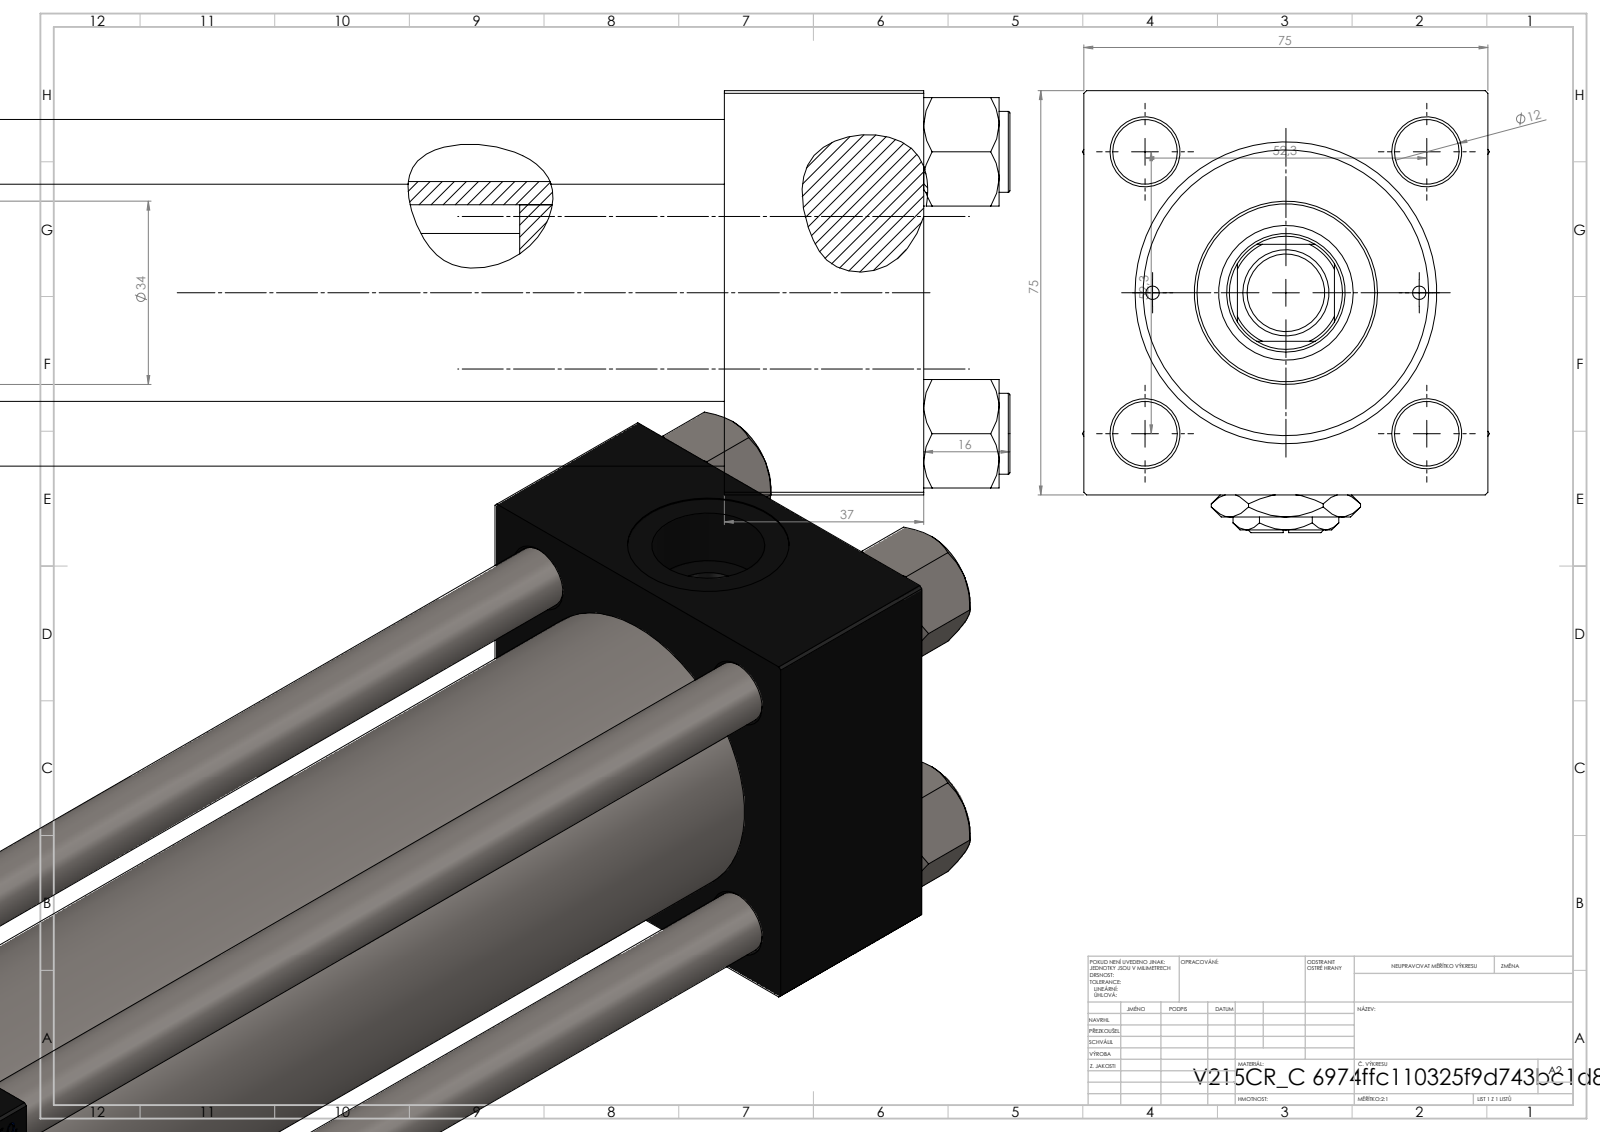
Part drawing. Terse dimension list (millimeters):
name: ROD_END_AH; V215_VC_A; NUT_M5_C; V215CR_C_Body (+3 more)
written by: SolidWorks 2019 (CONFIG_CONTROL_DESIGN)
unit: mm
bodies: 13 solids, 1216 faces (555 planar, 99 cylindrical, 562 other)
size: 357 × 82 × 75.54
volume: 844 145 mm³; area: 228 298 mm²
holes: 4× ⌀12, 2× ⌀2.5, 2× ⌀7, 2× ⌀20.96, 2× ⌀30, 1× ⌀10.5, 1× ⌀22, 1× ⌀25, 1× ⌀41, 1× ⌀50, 1× ⌀53
bosses: 4× ⌀15, 1× ⌀56, 1× ⌀34, 1× ⌀16, 1× ⌀14
rounds: 1× R10.5
face distances: 75, 37, 294, 257, 235, 59, 198, 265.3, 228.3, 30.3
hole spacings: 26.19, 36.98, 52.3, 57.22, 24.75, 73.96, 49.5, 233.5
